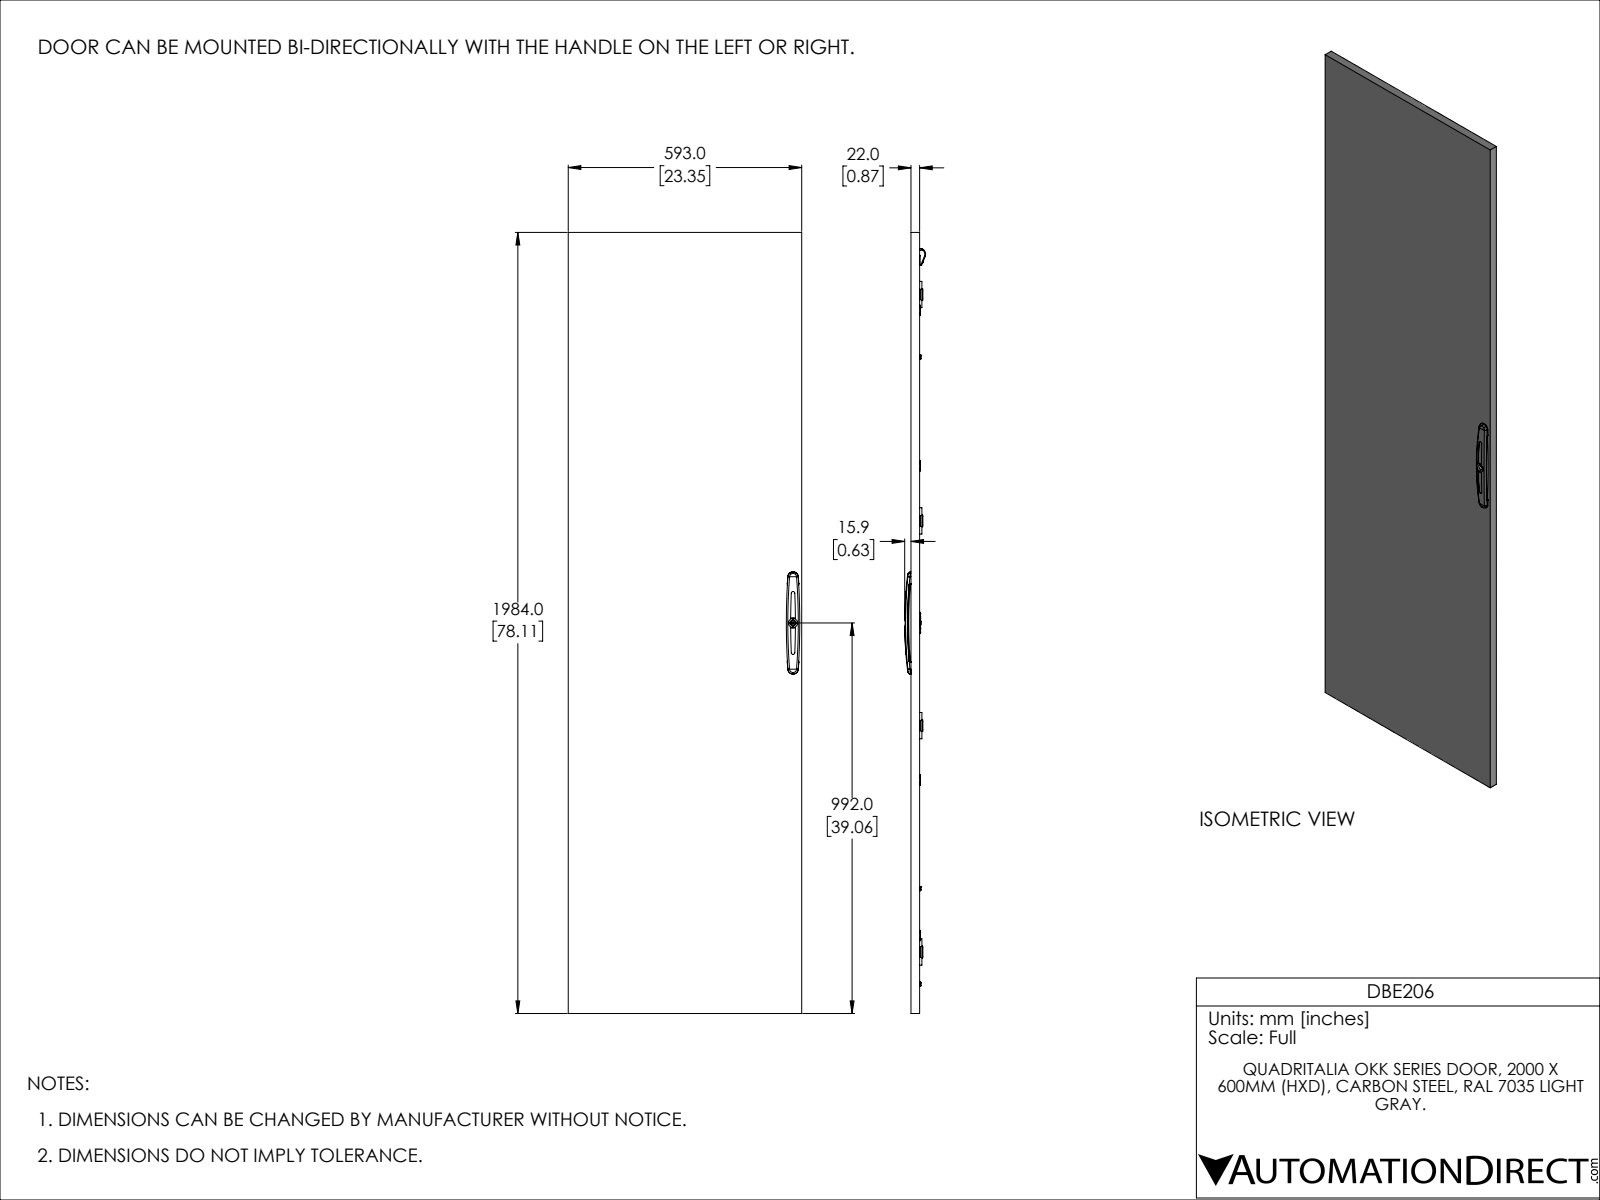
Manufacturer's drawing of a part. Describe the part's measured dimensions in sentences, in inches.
The part is named "DBE206". Its 3-D file was written by "SolidWorks 2021 (CONFIG_CONTROL_DESIGN)". It is 87 solids with 3289 faces: 1589 planar, 1169 cylindrical and 531 other. Overall it measures 78.11 by 23.346 by 2.091 inches. Its volume is 229.6 cubic inches and its surface area 5 672 square inches. Round holes: 144 of diameter 0.167, 18 of diameter 0.354, 8 of diameter 0.01, 8 of diameter 0.197, 6 of diameter 0.194, 4 of diameter 0.194, 4 of diameter 0.244, 4 of diameter 0.276, 3 of diameter 0.205, 2 of diameter 0.134, 2 of diameter 0.169, 2 of diameter 0.173. Round bosses or shafts: 23 of diameter 0.276, 19 of diameter 0.236, 10 of diameter 0.283, 8 of diameter 0.193, 2 of diameter 0.472, 2 of diameter 0.394, 2 of diameter 0.315, 2 of diameter 0.157. Partial cylindrical surfaces (rounded edges, fillets, slot ends): 74 of radius 0.012, 70 of radius 0.039, 36 of radius 0.059, 33 of radius 0.02, 28 of radius 0.098, 16 of radius 0.177, 15 of radius 0.079, 10 of radius 0.008. The main face-to-face distances are 0.079, 0.059, 0.728, 0.787, 0.669, 18.11, 0.866, 23.268, 0.138, 0.807. The hole center spacings are 0.984, 1.969, 2.953, 3.937, 4.921, 8.858, 5.906, 6.89.
